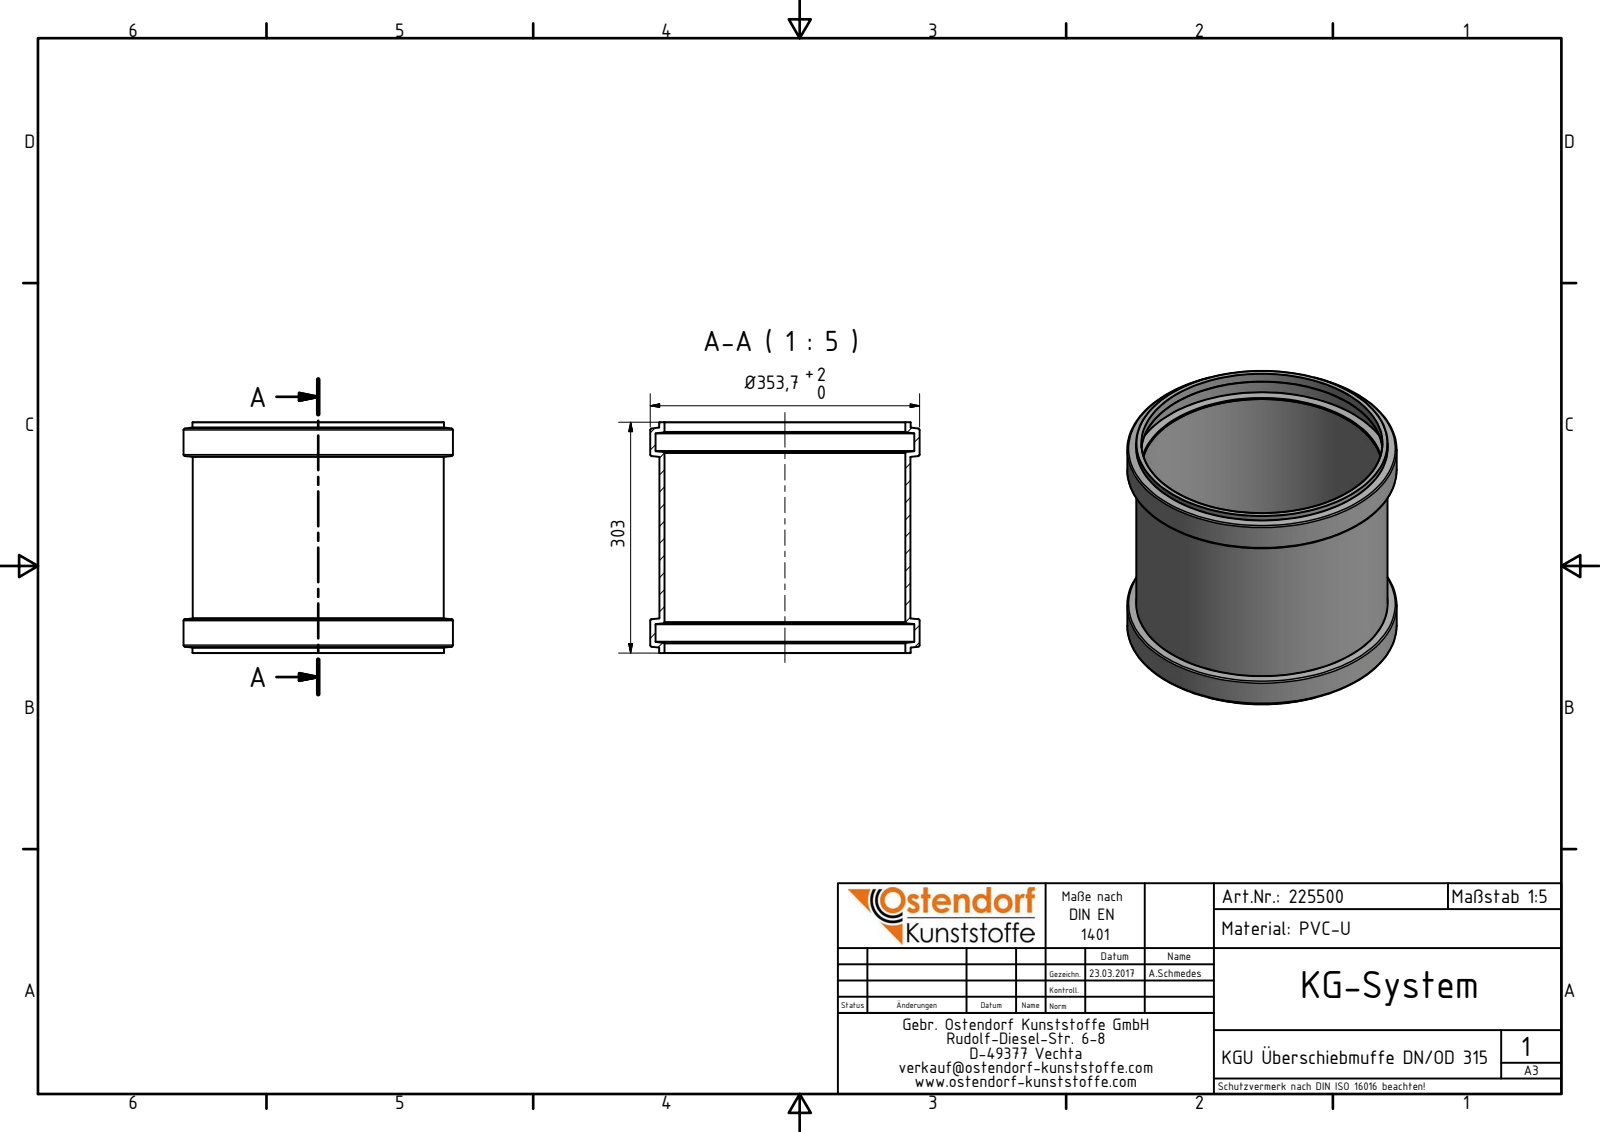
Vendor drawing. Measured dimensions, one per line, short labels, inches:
name: 225500 KGU Überschiebmuffe DN_OD 315
written by: Autodesk Inventor 2016 (AUTOMOTIVE_DESIGN)
unit: in
bodies: 1 solid, 44 faces (4 planar, 12 cylindrical, 28 other)
size: 13.925 × 13.925 × 11.929
volume: 150.1 in³; area: 1 118 in²
holes: 1× ⌀12.441, 1× ⌀12.453, 1× ⌀13.382
bosses: 1× ⌀13.925, 1× ⌀12.996, 1× ⌀12.984
face distances: 11.929, 1.596, 10.333, 8.736
